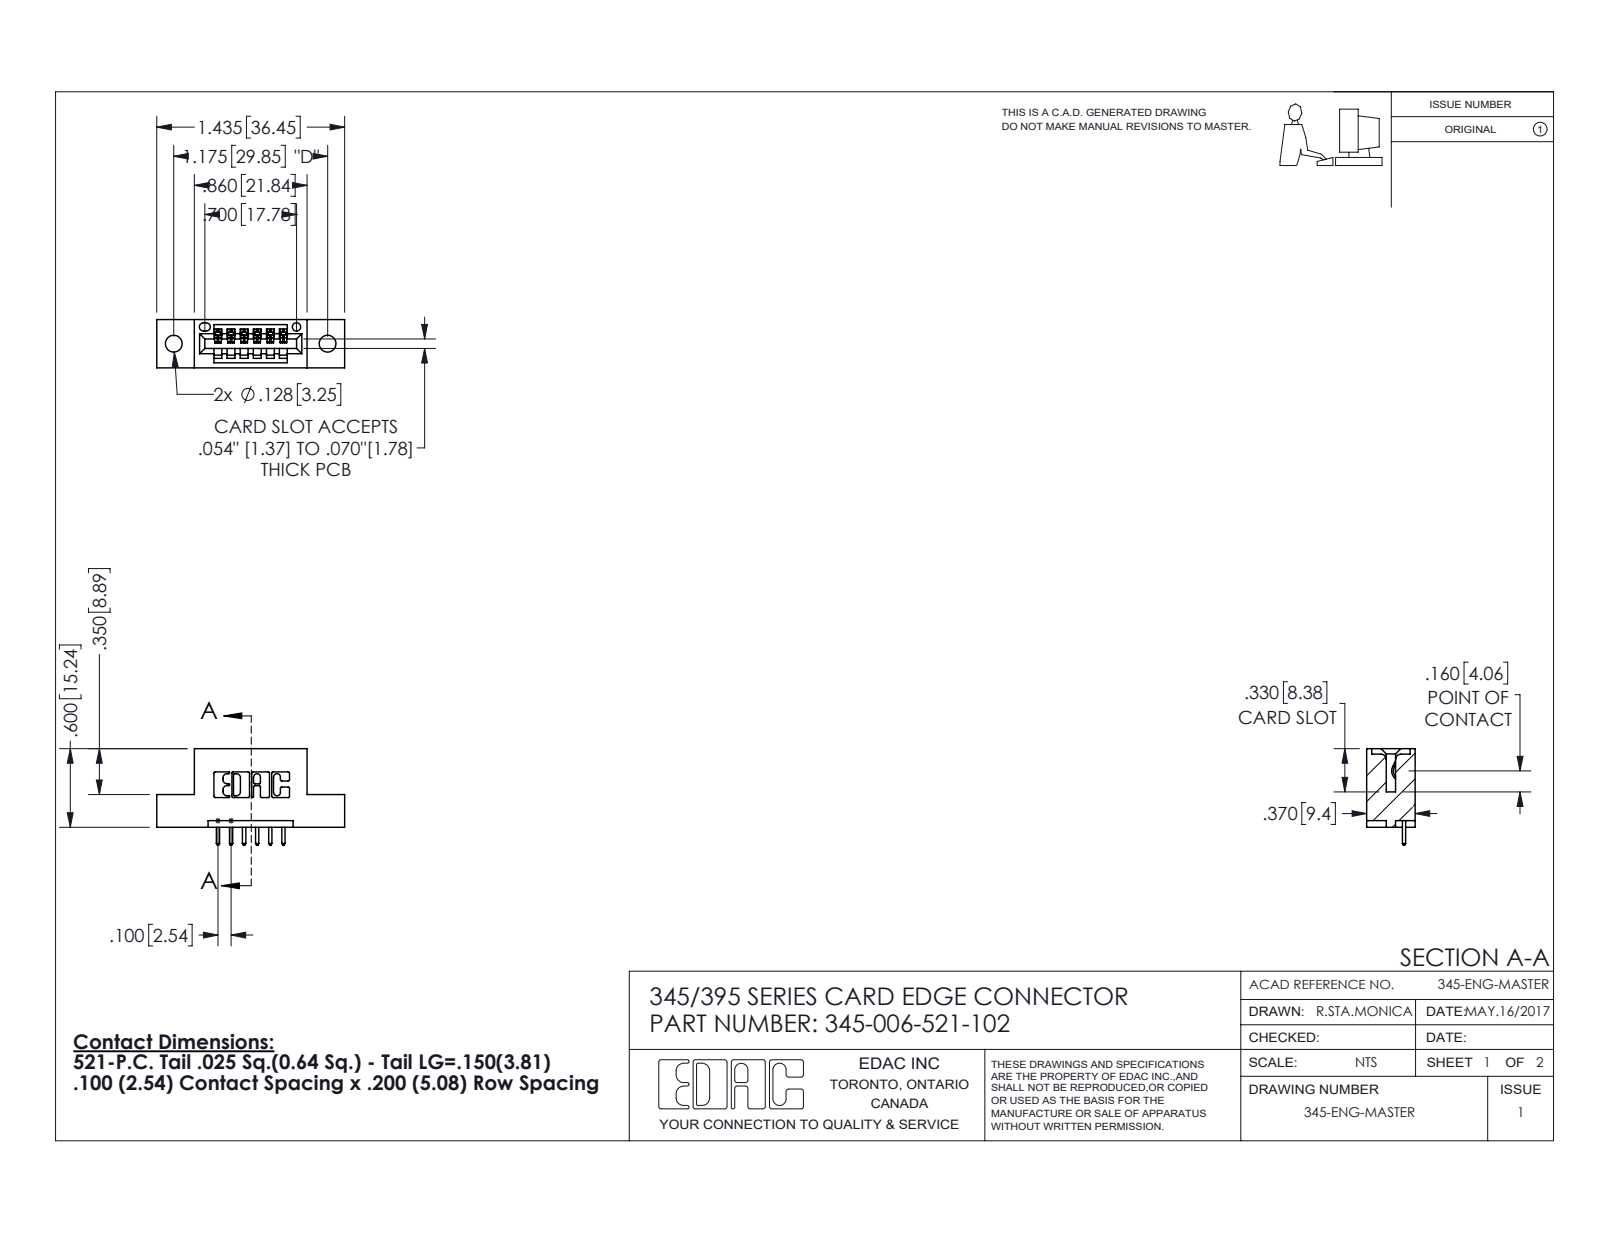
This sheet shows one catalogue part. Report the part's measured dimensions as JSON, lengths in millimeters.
{"part_name": "345-292-001_345-293-121; 345-006-521-102; 345 Part_Flush Mounting Lugs - 0.128 Dia", "step_written_by": "SolidWorks 2016 (CONFIG_CONTROL_DESIGN)", "units": "millimeters", "bodies": {"solids": 7, "faces": 474, "planar": 320, "cylindrical": 154, "other": 0}, "overall_size": [36.4, 18.7, 9.4], "volume_mm3": 3110, "surface_area_mm2": 3310, "round_holes": [[3.3, 2], [1.6, 1]], "partial_cylinders_radius": [[0.3, 22], [0.2, 12], [0.3, 12], [0.2, 6], [0.8, 6], [0.7, 3], [0.8, 2], [1, 2]], "face_to_face_distances": [5.1, 9.4, 7.6, 1.8, 2.5, 0.6, 2.5, 6.9, 1.5, 7.6], "hole_center_spacings": [6.9, 24, 29.8]}
